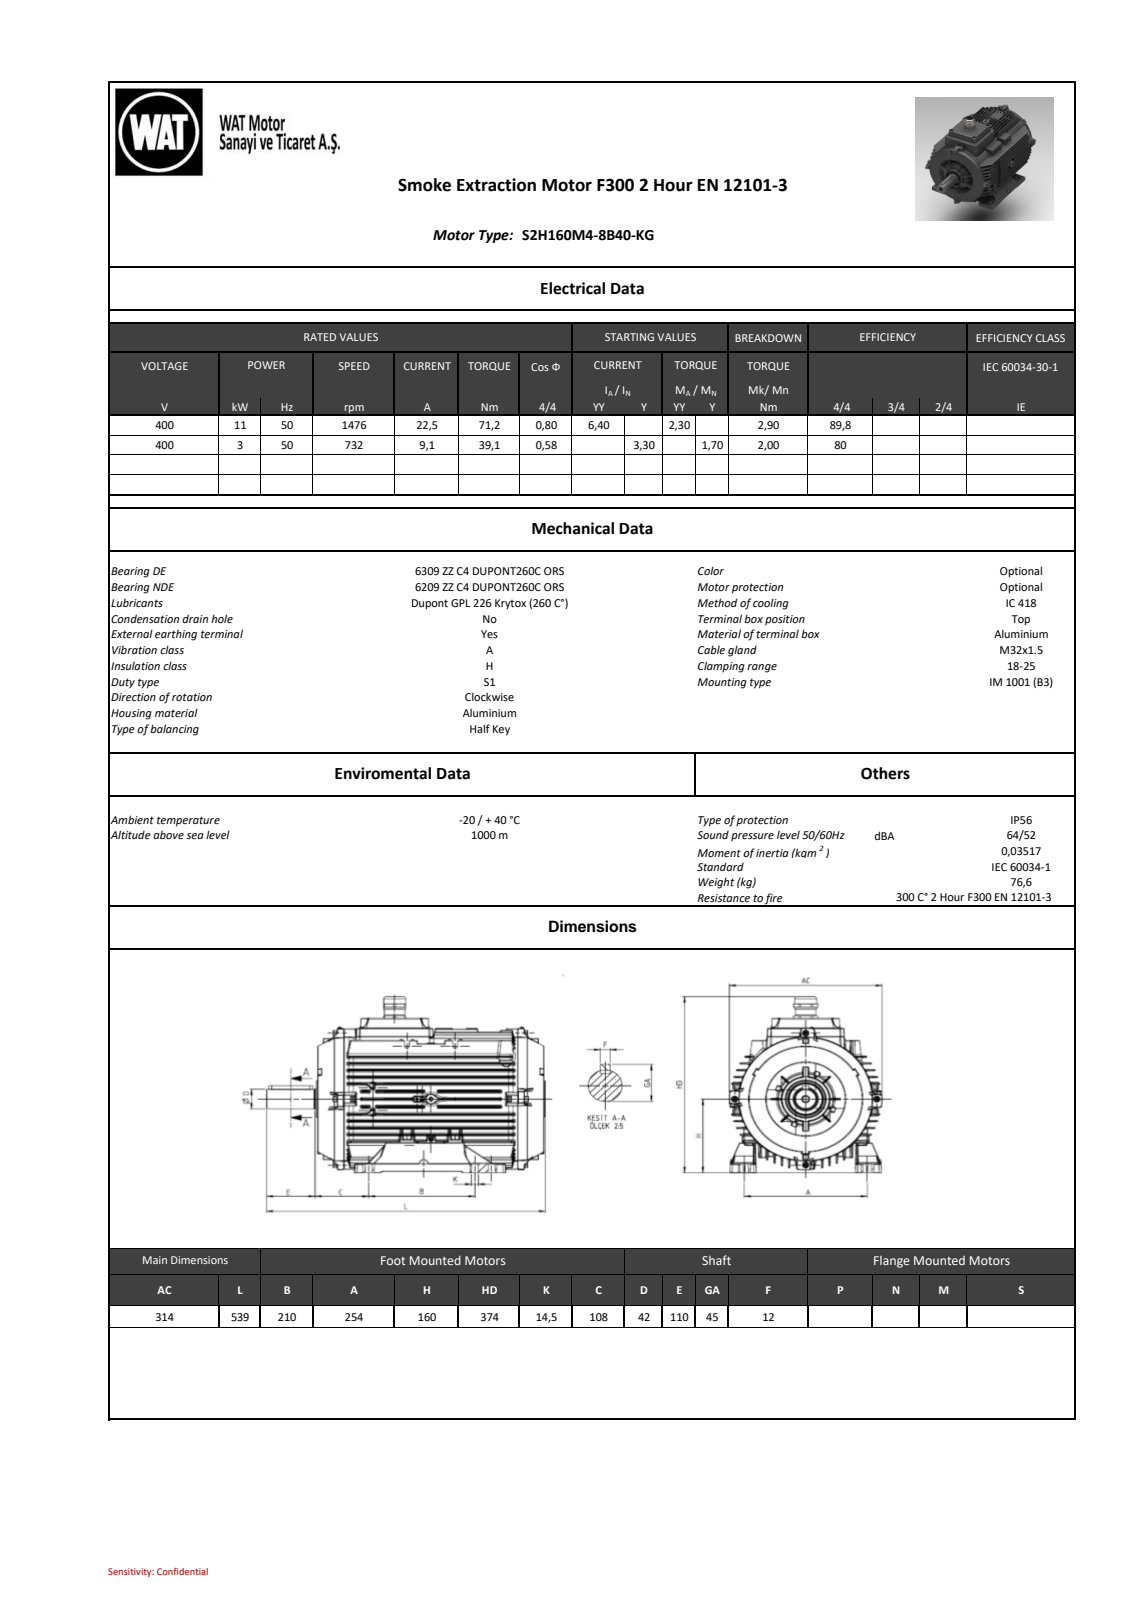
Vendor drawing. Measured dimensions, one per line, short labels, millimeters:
name: 26036A749124f13u
written by: SIEMENS PLM Software NX 11.0 (AP203_CONFIGURATION_CONTROLLED_3D_DESIGN_OF_MECHANICAL_PARTS_AND_ASSEMBLIES_MIM_LF)
unit: mm
bodies: 0 solids, 8265 faces (1766 planar, 2938 cylindrical, 3561 other)
size: 538.5 × 373.95 × 314
holes: 1× ⌀10.2, 1× ⌀13, 1× ⌀18, 1× ⌀54, 1× ⌀68.67
bosses: 4× ⌀14.8, 4× ⌀13, 4× ⌀10, 1× ⌀272.5, 1× ⌀72, 1× ⌀45, 1× ⌀42, 1× ⌀41.4
rounds: 782× R1, 762× R0.5, 107× R4, 77× R5, 50× R2.5, 13× R3, 8× R5.5, 8× R9
face distances: 11.85, 165.47, 9.32, 168, 2.53, 156.15, 144, 11.92, 21.47, 155.85
